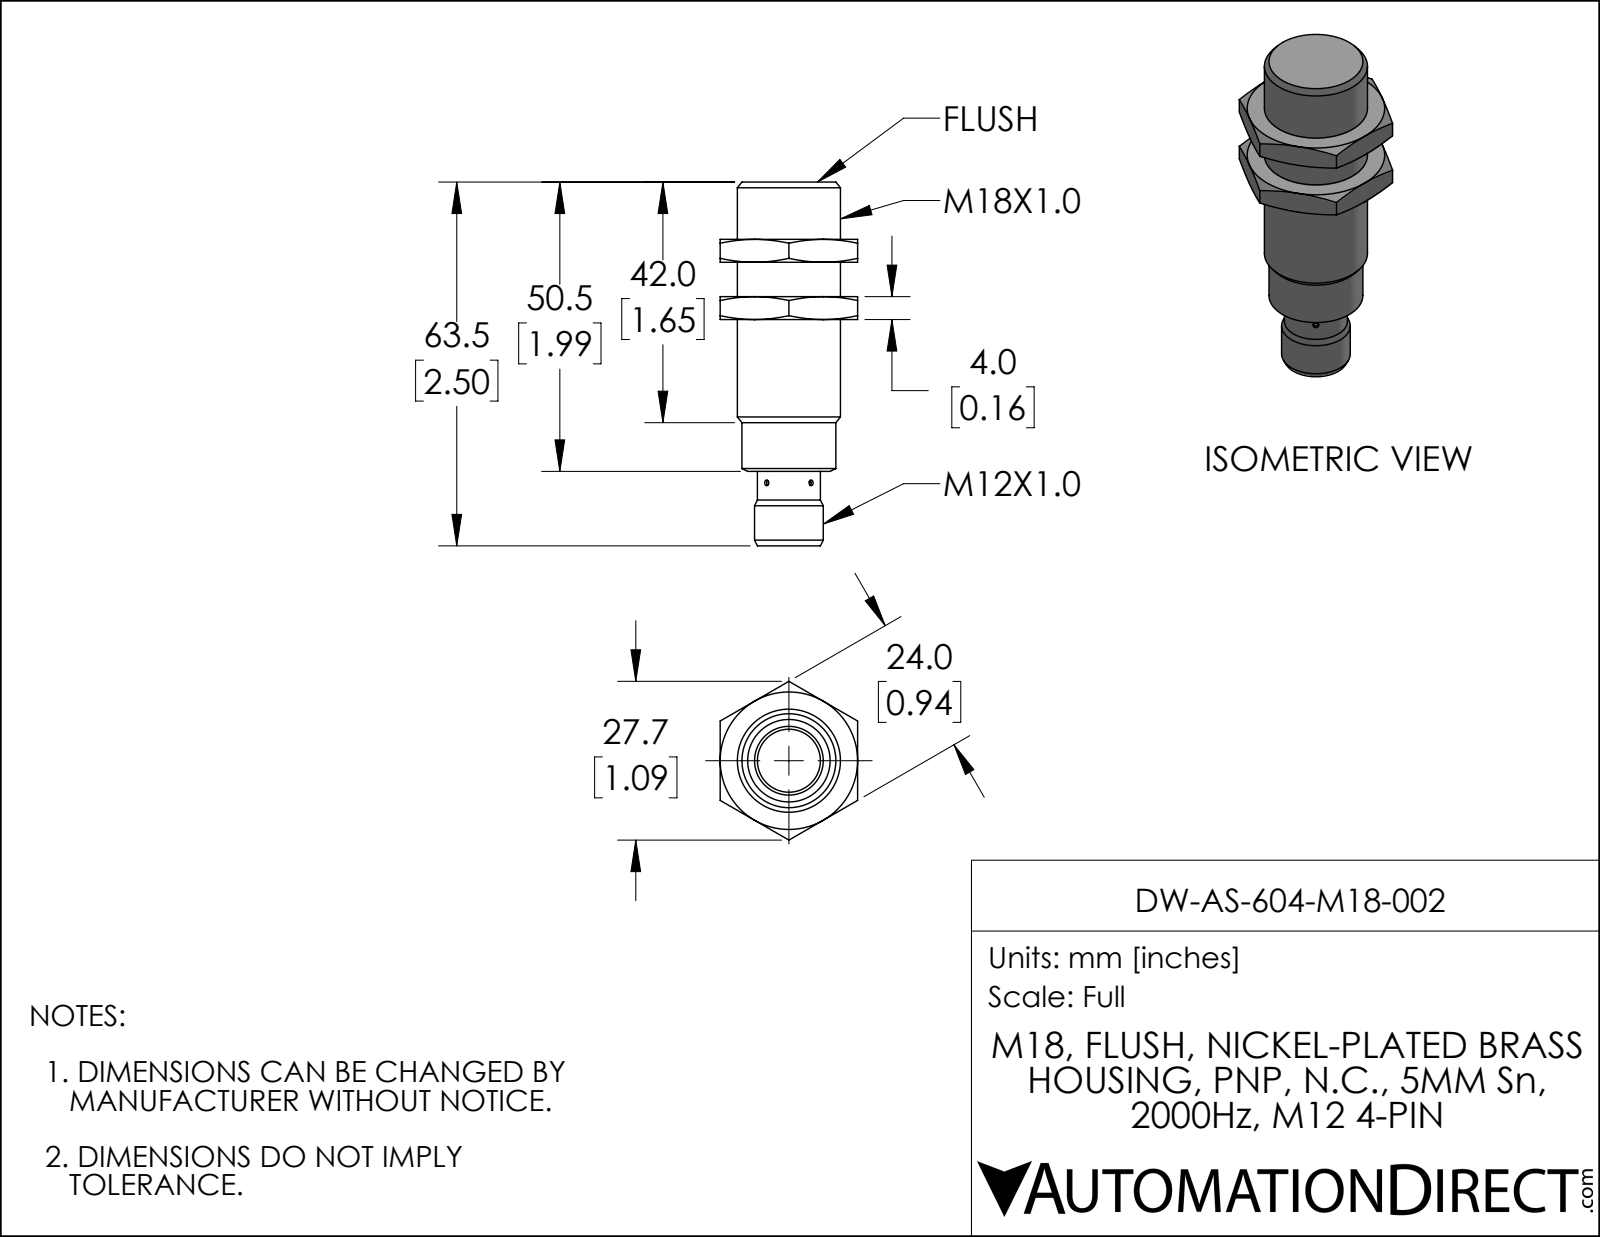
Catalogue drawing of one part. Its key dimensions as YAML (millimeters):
part_name: "DW-AS-604-M18-002"
step_written_by: "SolidWorks 2019 (AUTOMOTIVE_DESIGN)"
units: millimeters
bodies: {solids: 1, faces: 62, planar: 23, cylindrical: 10, other: 29}
overall_size: [63.5, 27.7, 24]
volume: 15700
surface_area: 4852
round_holes:
  - {diameter: 1, count: 2}
round_bosses_or_shafts:
  - {diameter: 18, count: 1}
  - {diameter: 16.4, count: 1}
  - {diameter: 12, count: 1}
  - {diameter: 11, count: 1}
face_to_face_distances: [10, 24, 14, 4, 20, 6, 63.5, 53.5, 49.5, 43.5]
